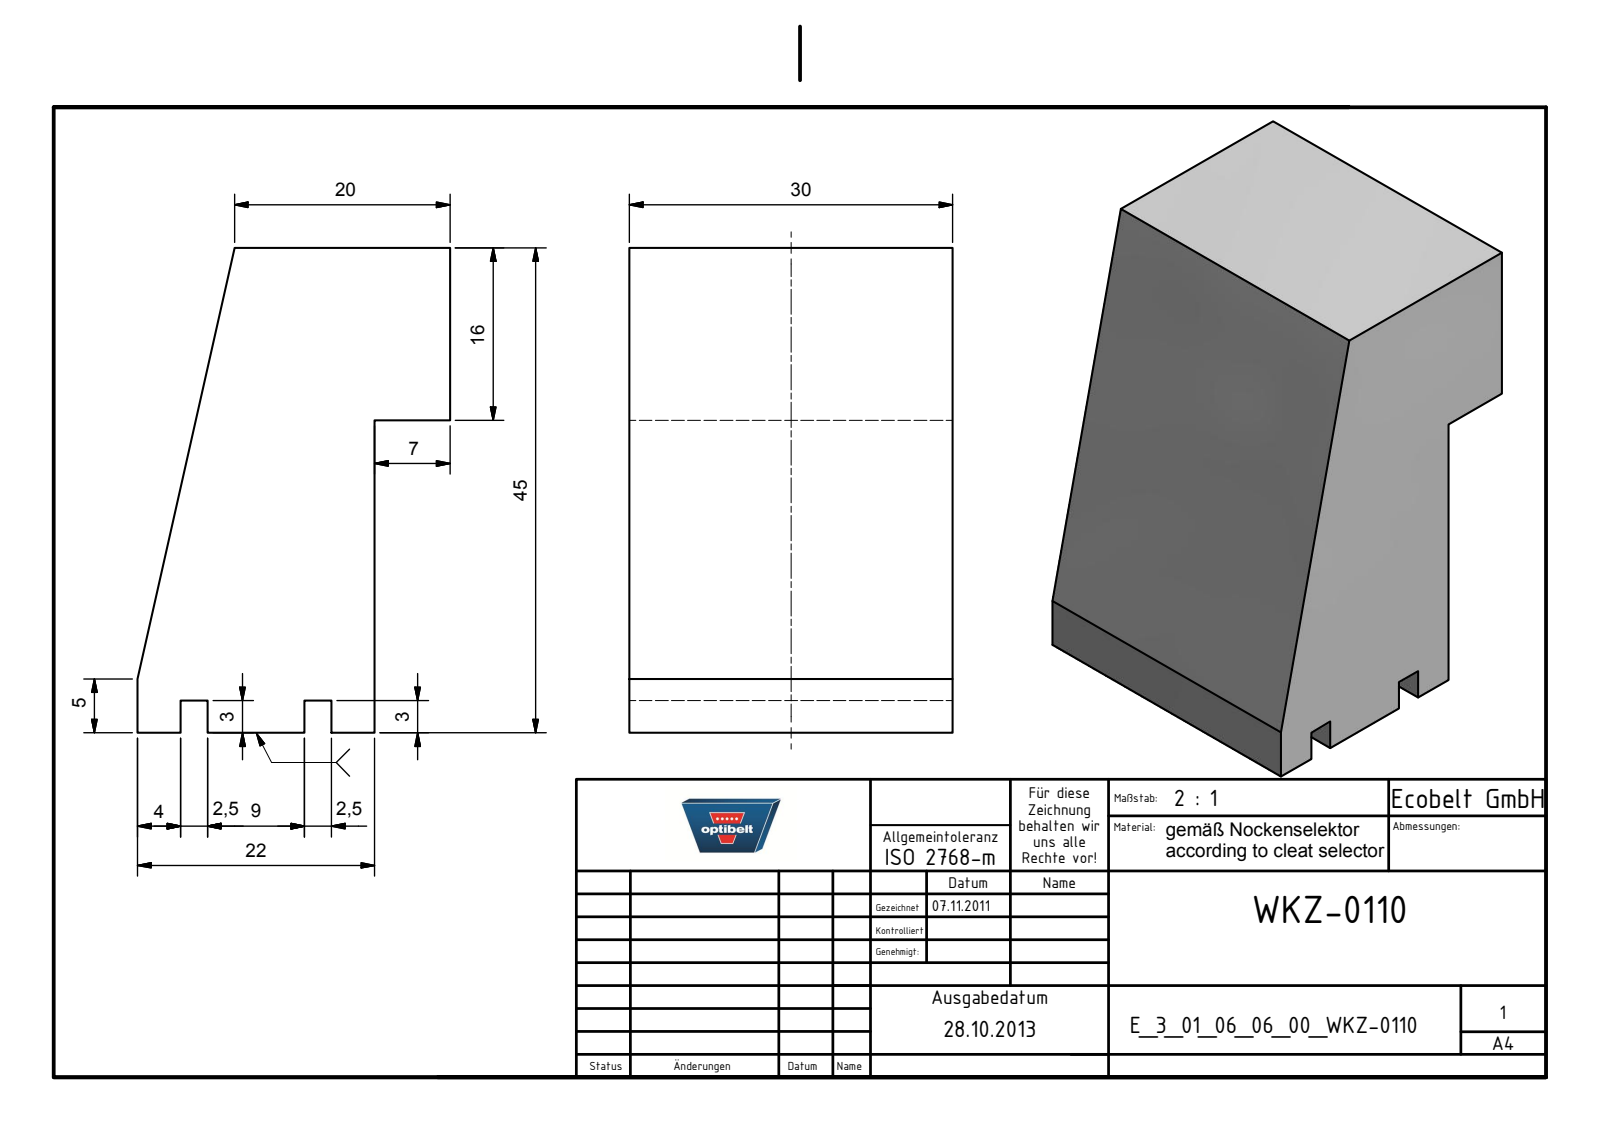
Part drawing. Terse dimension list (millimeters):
name: E_3_01_06_06_00_WKZ-0110
written by: Autodesk Inventor 2025 (AUTOMOTIVE_DESIGN)
unit: mm
bodies: 1 solid, 17 faces (17 planar, 0 cylindrical, 0 other)
size: 45 × 30 × 29
volume: 27 210 mm³; area: 6 374 mm²
face distances: 30, 45, 7, 29, 16, 4, 6.5, 15.5, 18, 2.5
